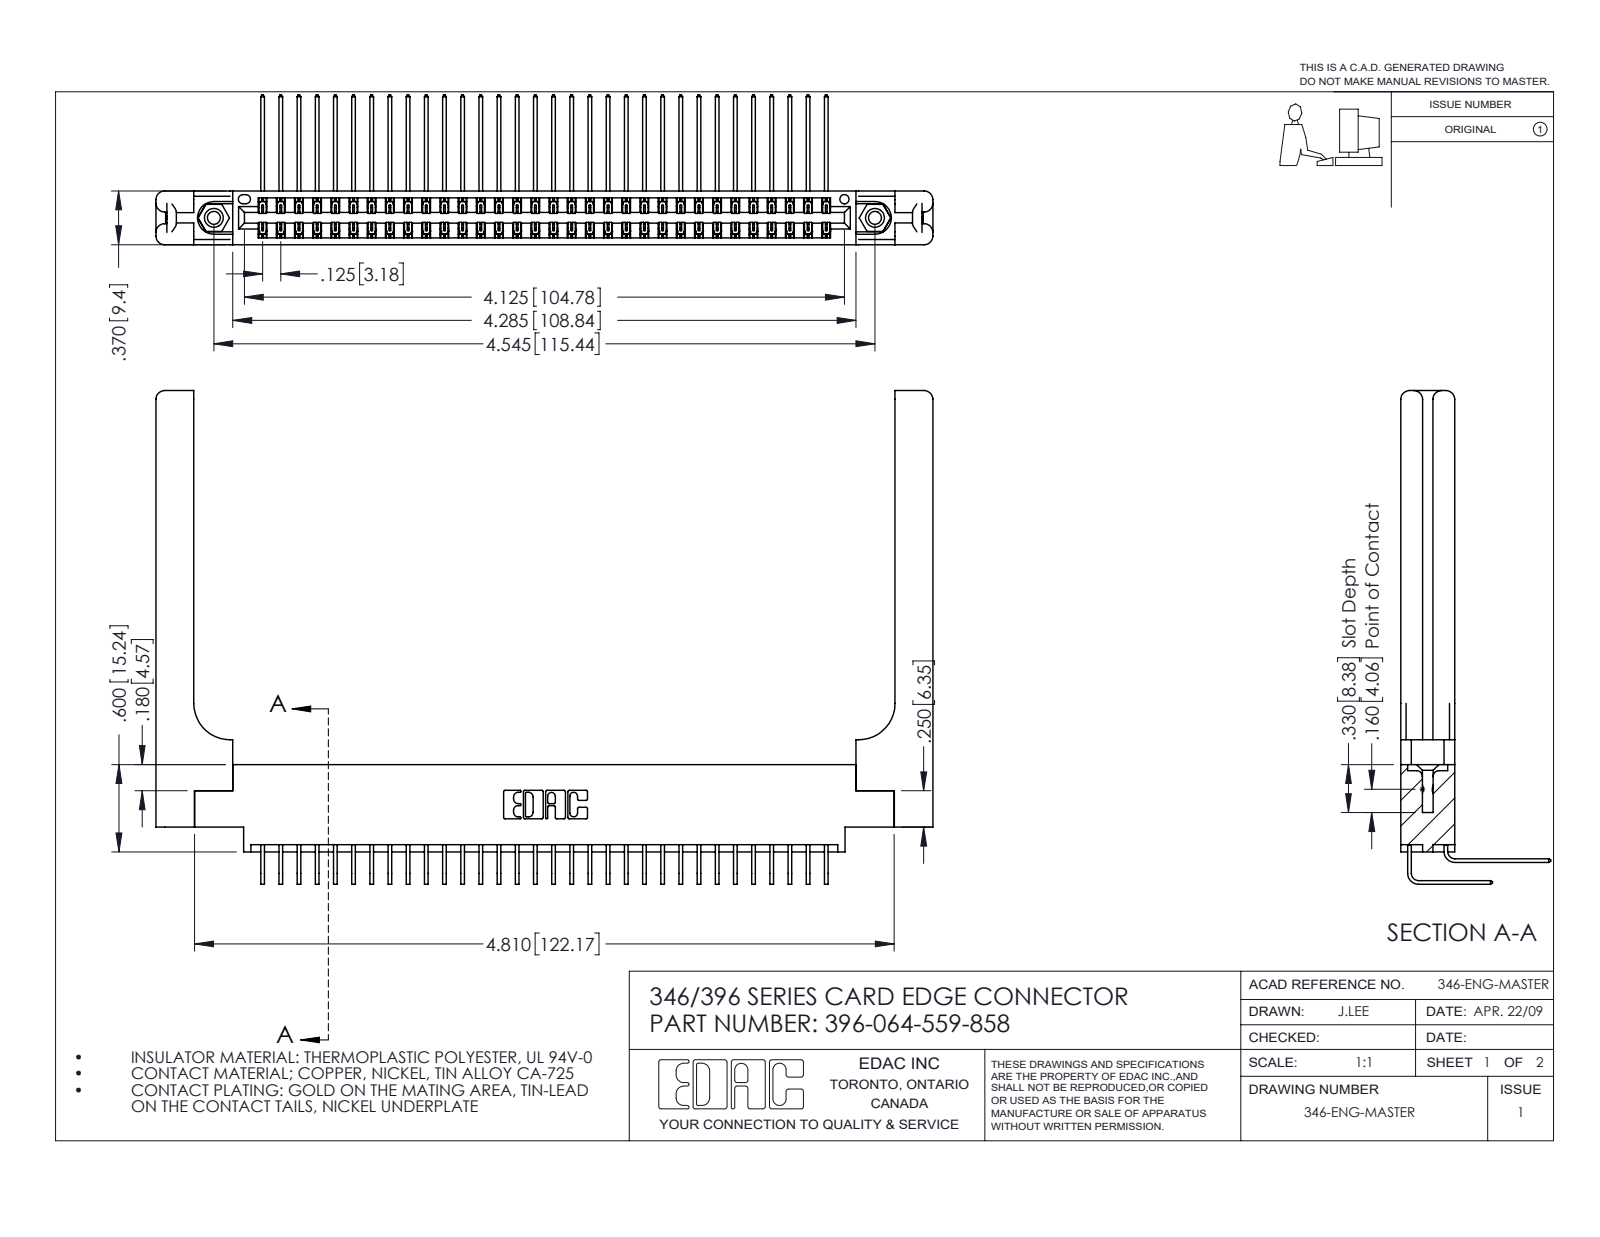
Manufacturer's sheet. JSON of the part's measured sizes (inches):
{"part_name": "346 Part_0.170 Offset - 0.156 Dia-TH; 345-292-001_559 Tail - 2; 345-250-001_345-250-001-102; 396-064-559-858 (+2 more)", "step_written_by": "SolidWorks 2016 (CONFIG_CONTROL_DESIGN)", "units": "inches", "bodies": {"solids": 69, "faces": 3838, "planar": 2596, "cylindrical": 1182, "other": 60}, "overall_size": [5.341, 3.393, 1.03], "volume_in3": 1.273, "surface_area_in2": 38.96, "round_holes": [[0.089, 2], [0.125, 2], [0.156, 2], [0.064, 1]], "round_bosses_or_shafts": [[0.155, 2]], "partial_cylinders_radius": [[0.006, 96], [0.01, 22], [0.06, 16], [0.007, 6], [0.031, 6], [0.026, 3], [0.014, 2], [0.022, 2]], "face_to_face_distances": [0.37, 0.048, 0.072, 0.322, 0.025, 0.148, 0.15, 0.25, 0.298, 0.275], "hole_center_spacings": [0.246, 4.337, 4.545]}
